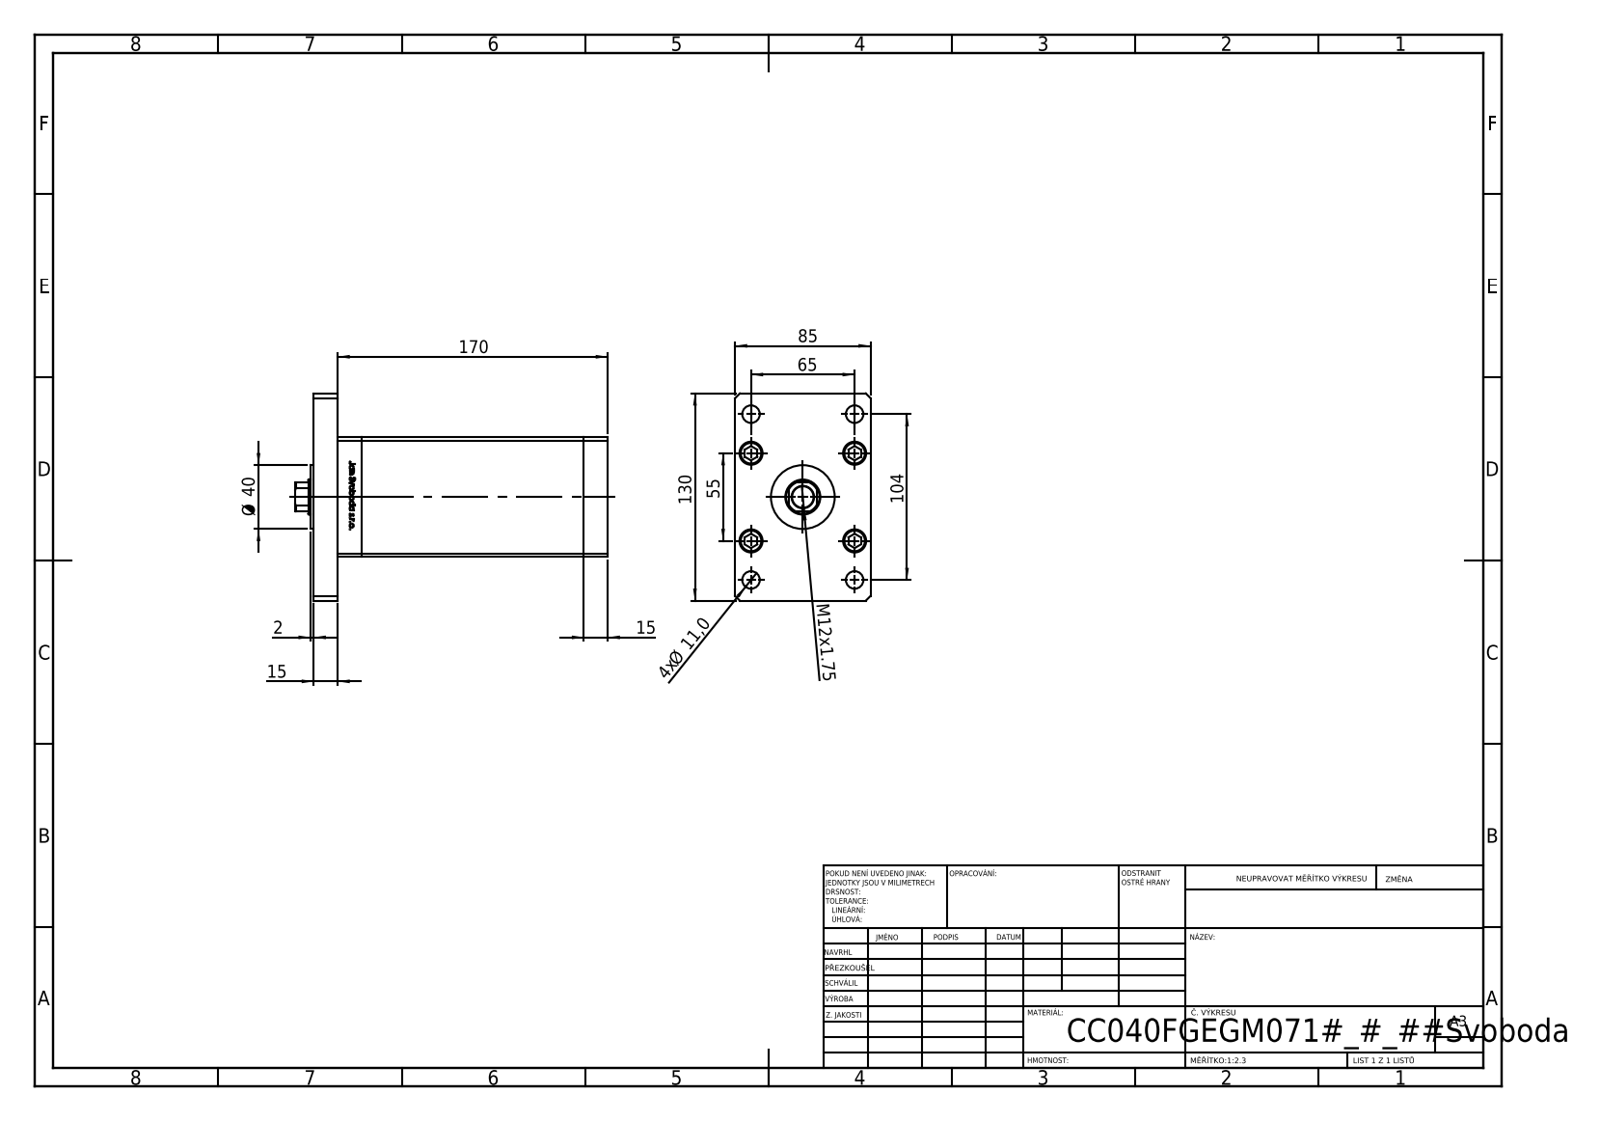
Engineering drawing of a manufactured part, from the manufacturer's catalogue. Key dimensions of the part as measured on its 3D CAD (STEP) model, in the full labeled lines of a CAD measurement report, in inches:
Part name (STEP PRODUCT): V220C_FRONT_F; V220C_F; V220C_F_MIDDLE; ALLEN BOLT (+2 more)
STEP written by: SolidWorks 2019 (CONFIG_CONTROL_DESIGN)
Units: inches
Bodies: 19 solids, 1310 faces (517 planar, 187 cylindrical, 606 other)
Overall size (bounding box): 7.717 × 5.118 × 3.346
Volume: 68.22 in³ · Surface area: 300.8 in²
Round holes (diameter × count): ⌀0.433 ×9, ⌀0.61 ×5, ⌀0.394 ×4, ⌀0.571 ×4, ⌀0.079 ×2, ⌀0.518 ×2, ⌀0.531 ×1, ⌀0.866 ×1, ⌀0.925 ×1
Round bosses / shafts (diameter × count): ⌀0.315 ×9, ⌀0.571 ×5, ⌀1.575 ×1
Partial cylindrical surfaces — rounded edges, fillets, slot ends (radius × count): R0.037 ×2, R0.413 ×1
Main face-to-face distances: 0.591, 6.083, 6.673, 3.346, 2.953, 1.181, 5.492, 7.264, 0.413, 1.083
Hole centre spacings: 1.102, 0.965, 1.676, 2.414, 2.559, 2.735, 3.13, 4.043
